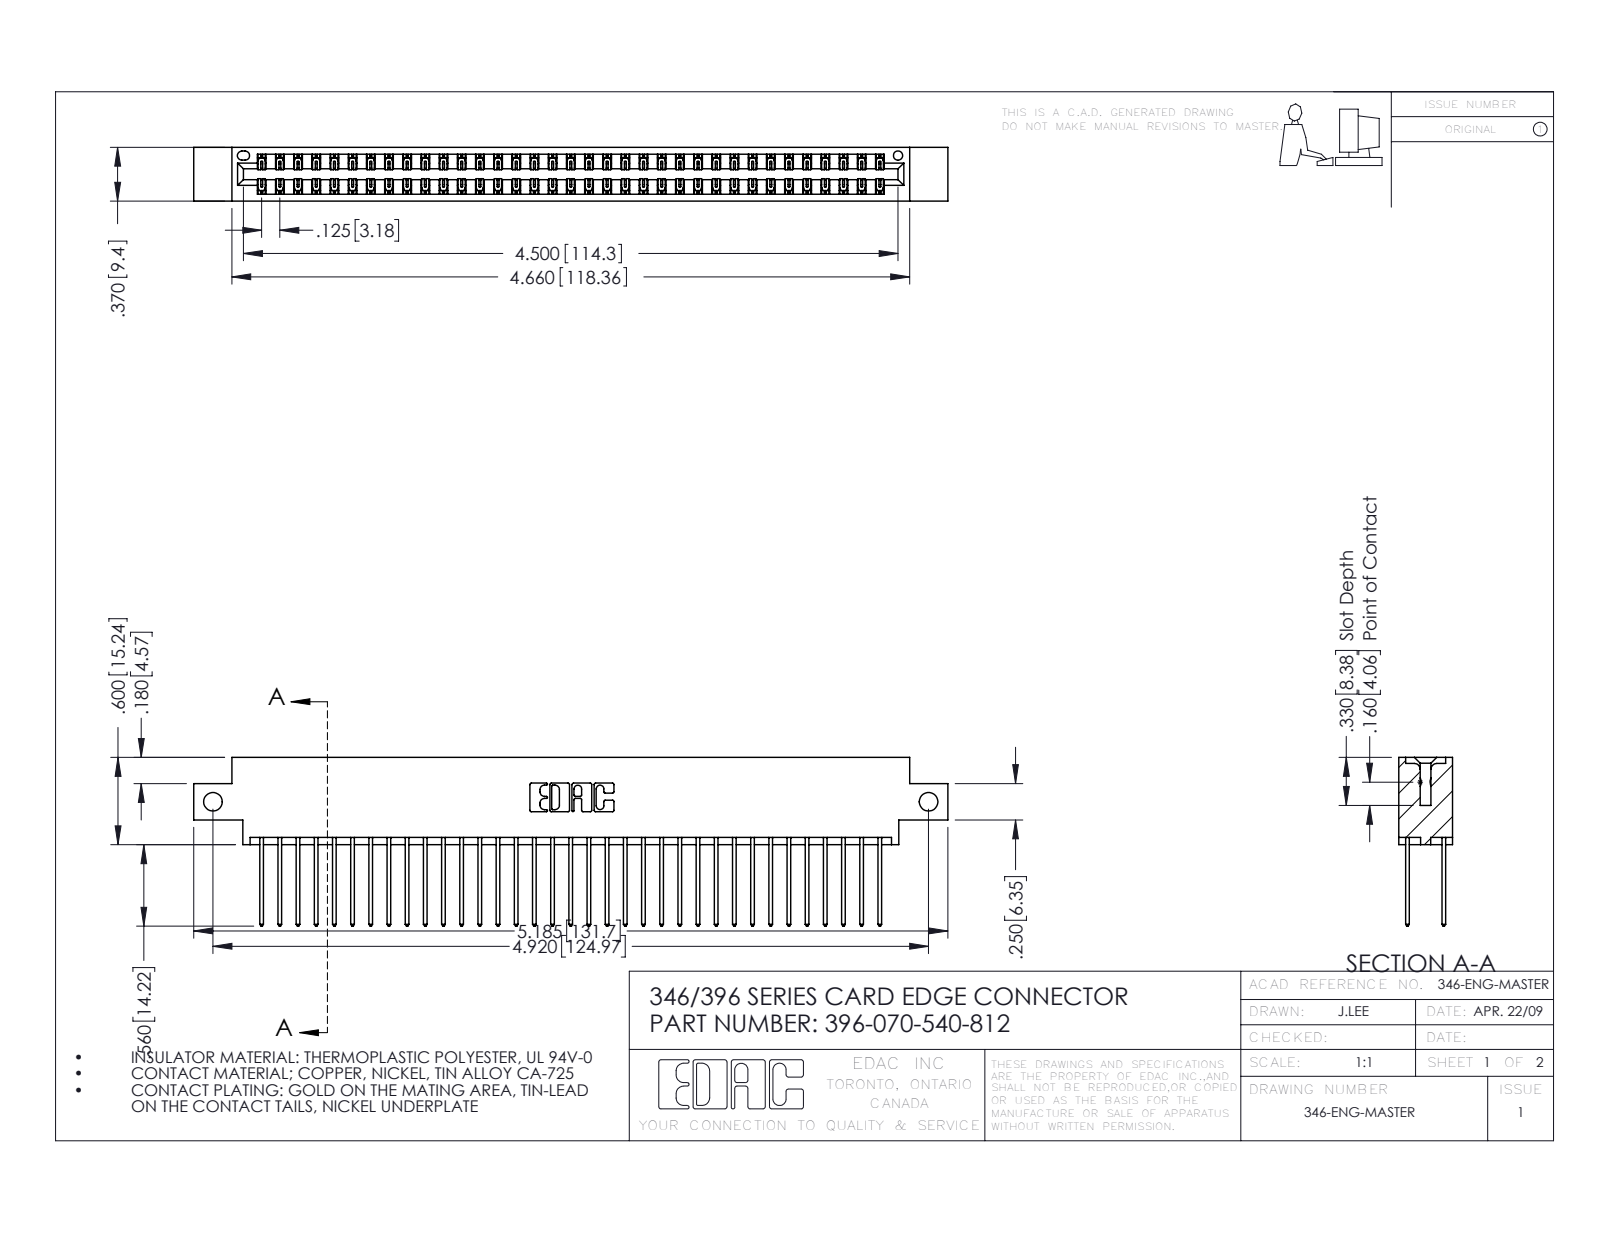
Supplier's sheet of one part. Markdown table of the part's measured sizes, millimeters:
| quantity | value |
| --- | --- |
| part name | 345-292-001_345-293-140; 346 Part_0.170 Offset - Side Mount; 396-070-540-812 |
| STEP written by | SolidWorks 2016 (CONFIG_CONTROL_DESIGN) |
| units | millimeters |
| bodies | 71 solids, 3766 faces (2530 planar, 1236 cylindrical, 0 other) |
| overall size | 131.7 × 29.5 × 9.4 |
| volume | 12 800 mm³ |
| surface area | 18 800 mm² |
| round holes (diameter × count) | 3.3 × 2, 1.6 × 1 |
| partial cylindrical surfaces (radius × count) | 0.2 × 105, 0.3 × 70, 0.3 × 22, 0.2 × 6, 0.8 × 6, 0.7 × 3, 0.4 × 2, 0.6 × 2 |
| main face-to-face distances | 1.2, 8.2, 6.4, 1.8, 7.6, 0.6, 9.4, 7, 3.8, 5.6 |
| hole center spacings | 125 |
